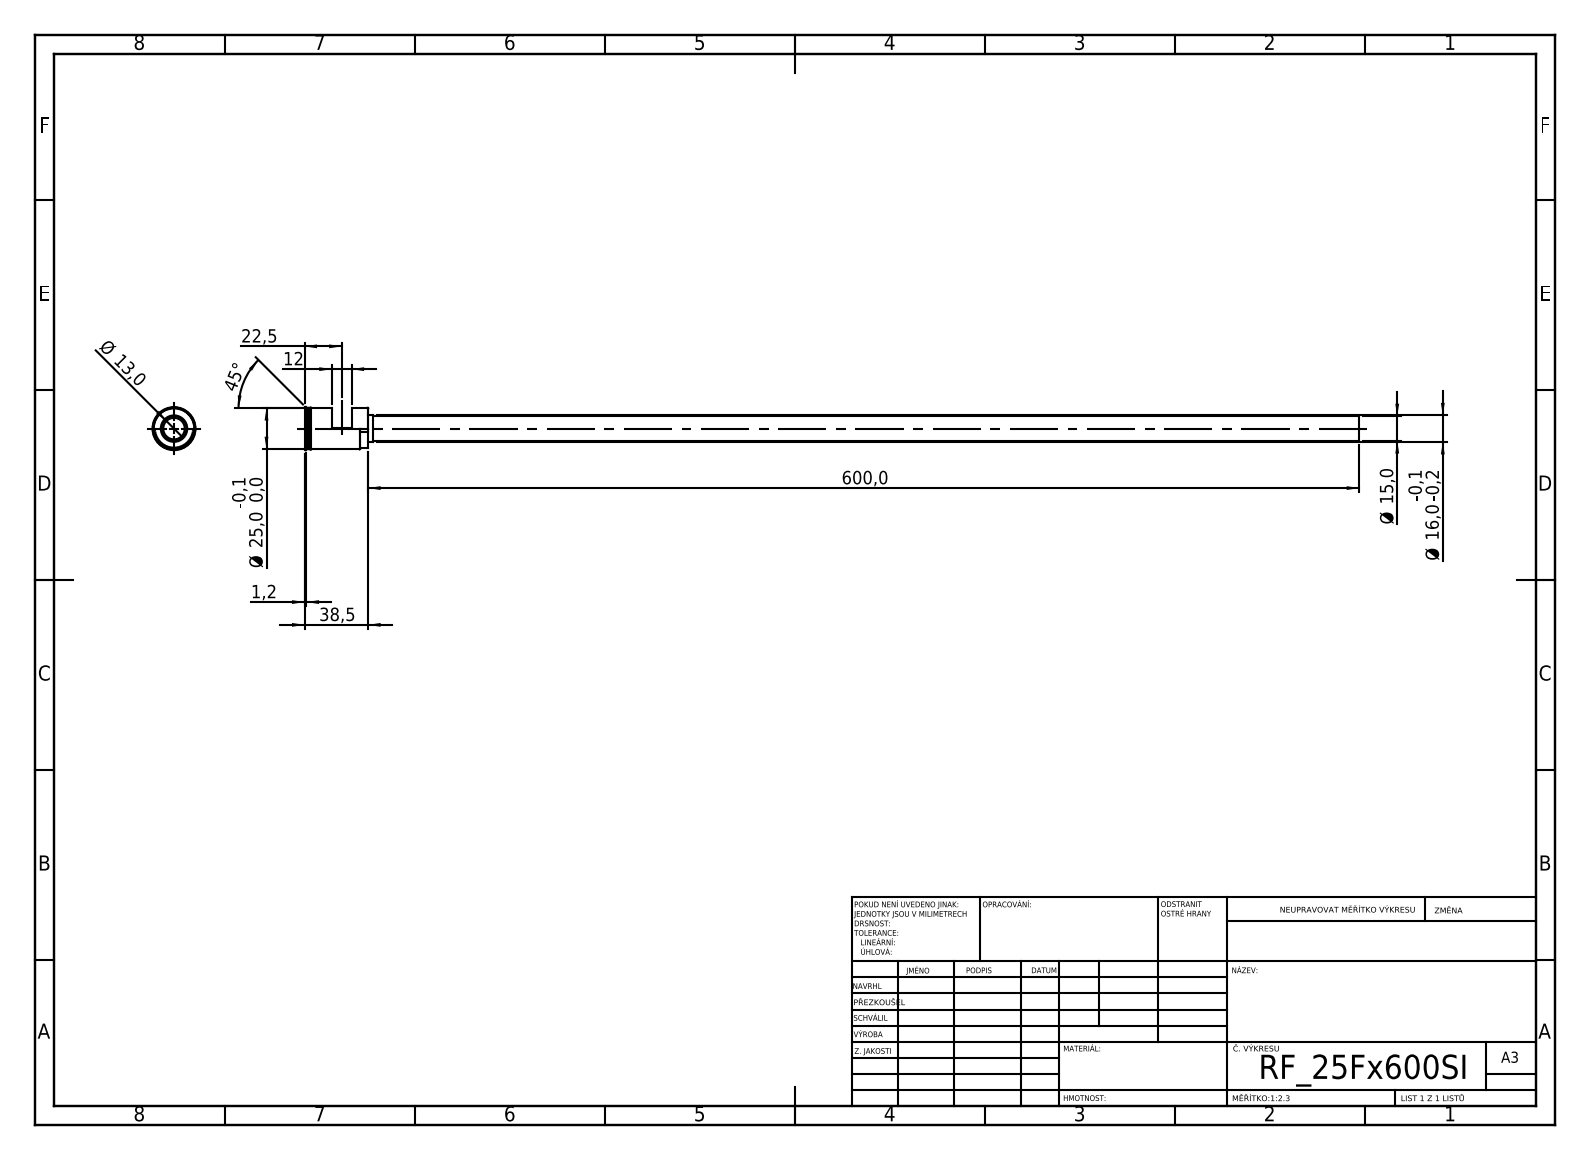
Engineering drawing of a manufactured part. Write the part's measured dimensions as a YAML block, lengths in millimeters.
step_written_by: "SolidWorks 2019 (CONFIG_CONTROL_DESIGN)"
units: millimeters
bodies: {solids: 1, faces: 55, planar: 24, cylindrical: 19, other: 12}
overall_size: [638.5, 26, 26]
volume: 39485
surface_area: 57713
round_holes:
  - {diameter: 13, count: 1}
round_bosses_or_shafts:
  - {diameter: 26, count: 1}
  - {diameter: 25, count: 1}
  - {diameter: 24.8, count: 1}
  - {diameter: 16, count: 1}
  - {diameter: 15, count: 1}
partial_cylinders:
  - {radius: 3, count: 2}
  - {radius: 11.55, count: 1}
face_to_face_distances: [14.5, 22, 36.5, 10, 12, 26.5, 2, 38.5, 28.5, 16.5]
